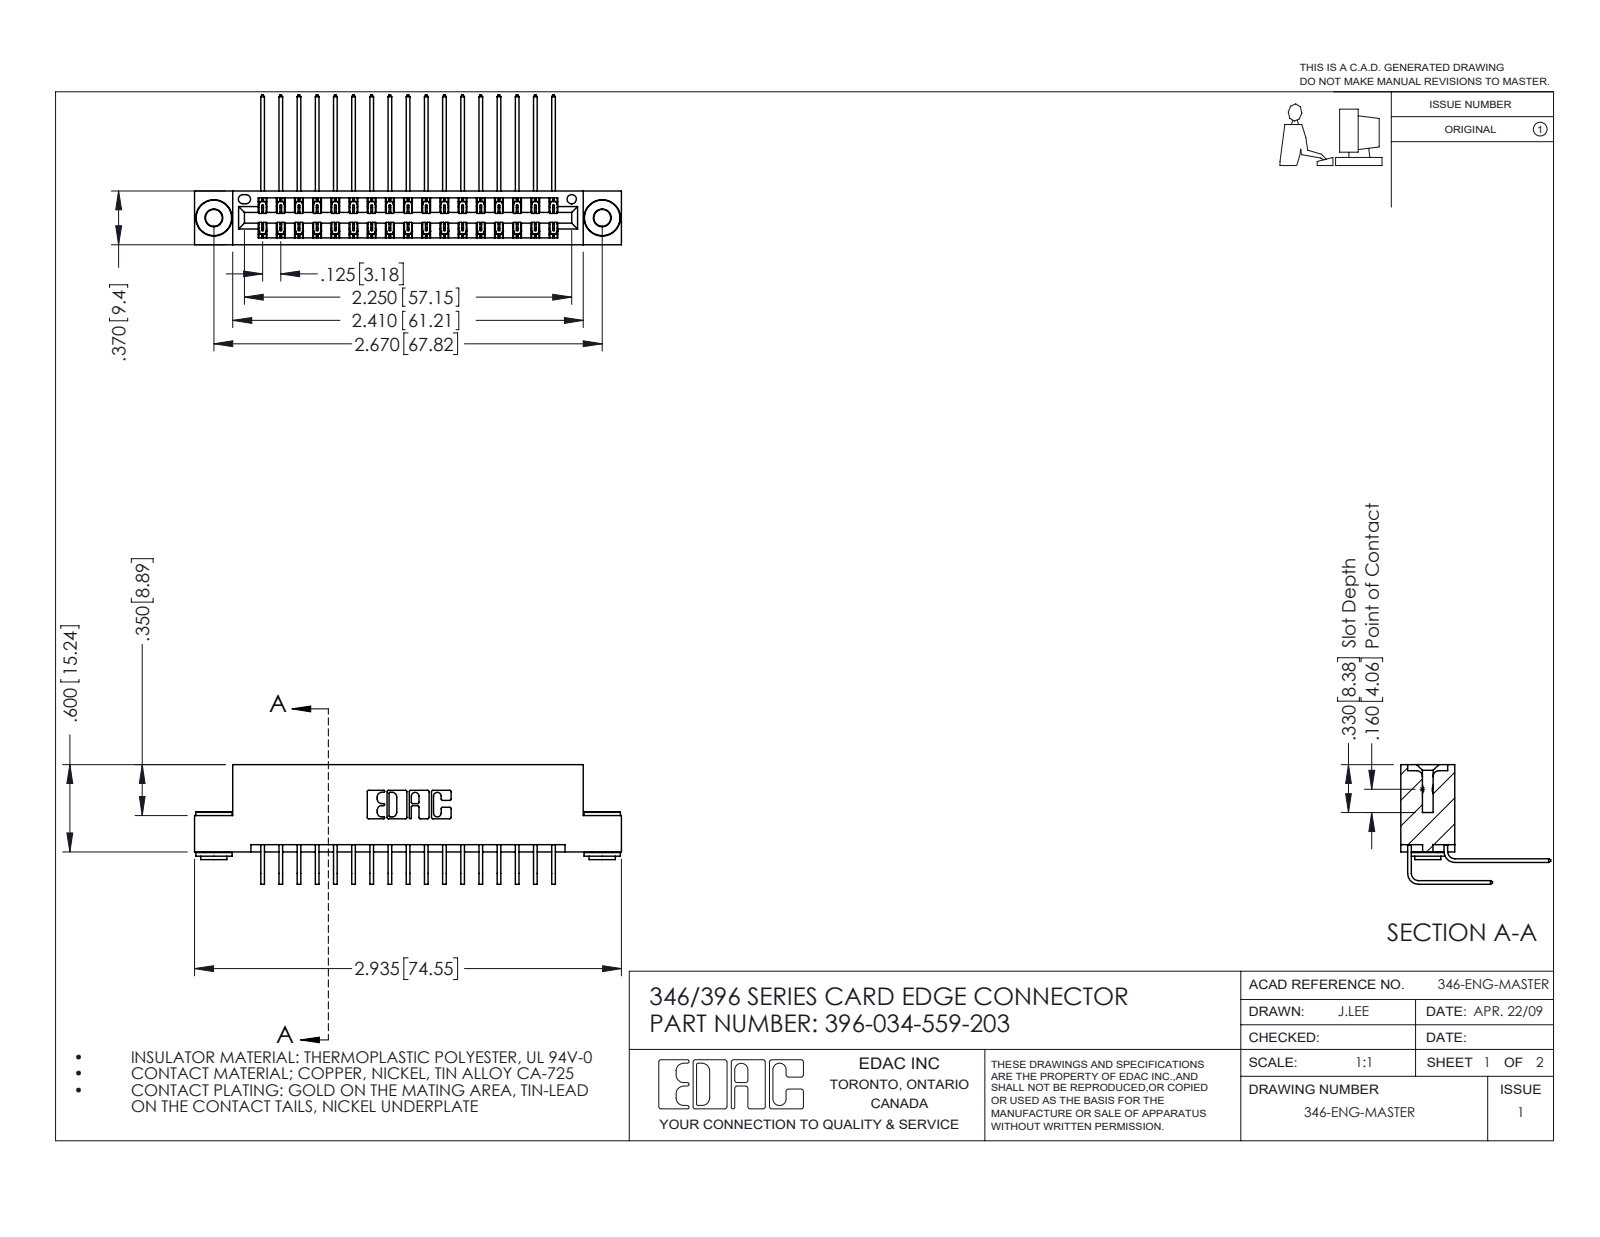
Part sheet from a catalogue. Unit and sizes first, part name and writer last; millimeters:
Units: millimetres
Overall size (bounding box): 74.5 × 26.2 × 20.9
Round holes (diameter × count): ⌀2.9 ×2, ⌀4 ×2, ⌀1.6 ×1
Round bosses / shafts (diameter × count): ⌀6.4 ×2, ⌀4.6 ×2, ⌀3.5 ×2
Partial cylindrical surfaces — rounded edges, fillets, slot ends (radius × count): R0.2 ×51, R0.3 ×22, R0.2 ×6, R0.8 ×6, R0.7 ×3, R0.4 ×2, R0.6 ×2, R0.6 ×2
Main face-to-face distances: 1.2, 8.2, 6.4, 0.6, 9.4, 1.8, 7.6, 7, 3.8, 5.6
Hole centre spacings: 6.2, 62.6, 67.8
Volume: 7 290 mm³ · Surface area: 10 790 mm²
Bodies: 37 solids, 1996 faces (1344 planar, 644 cylindrical, 8 other)
Part name (STEP PRODUCT): 396-034-559-203; 345-250-002_345-250-002-102; 345-292-001_559 Tail - 2; 346 Part_Flush Mounting Lugs - 0.156 Dia-TH (+1 more)
STEP written by: SolidWorks 2016 (CONFIG_CONTROL_DESIGN)
